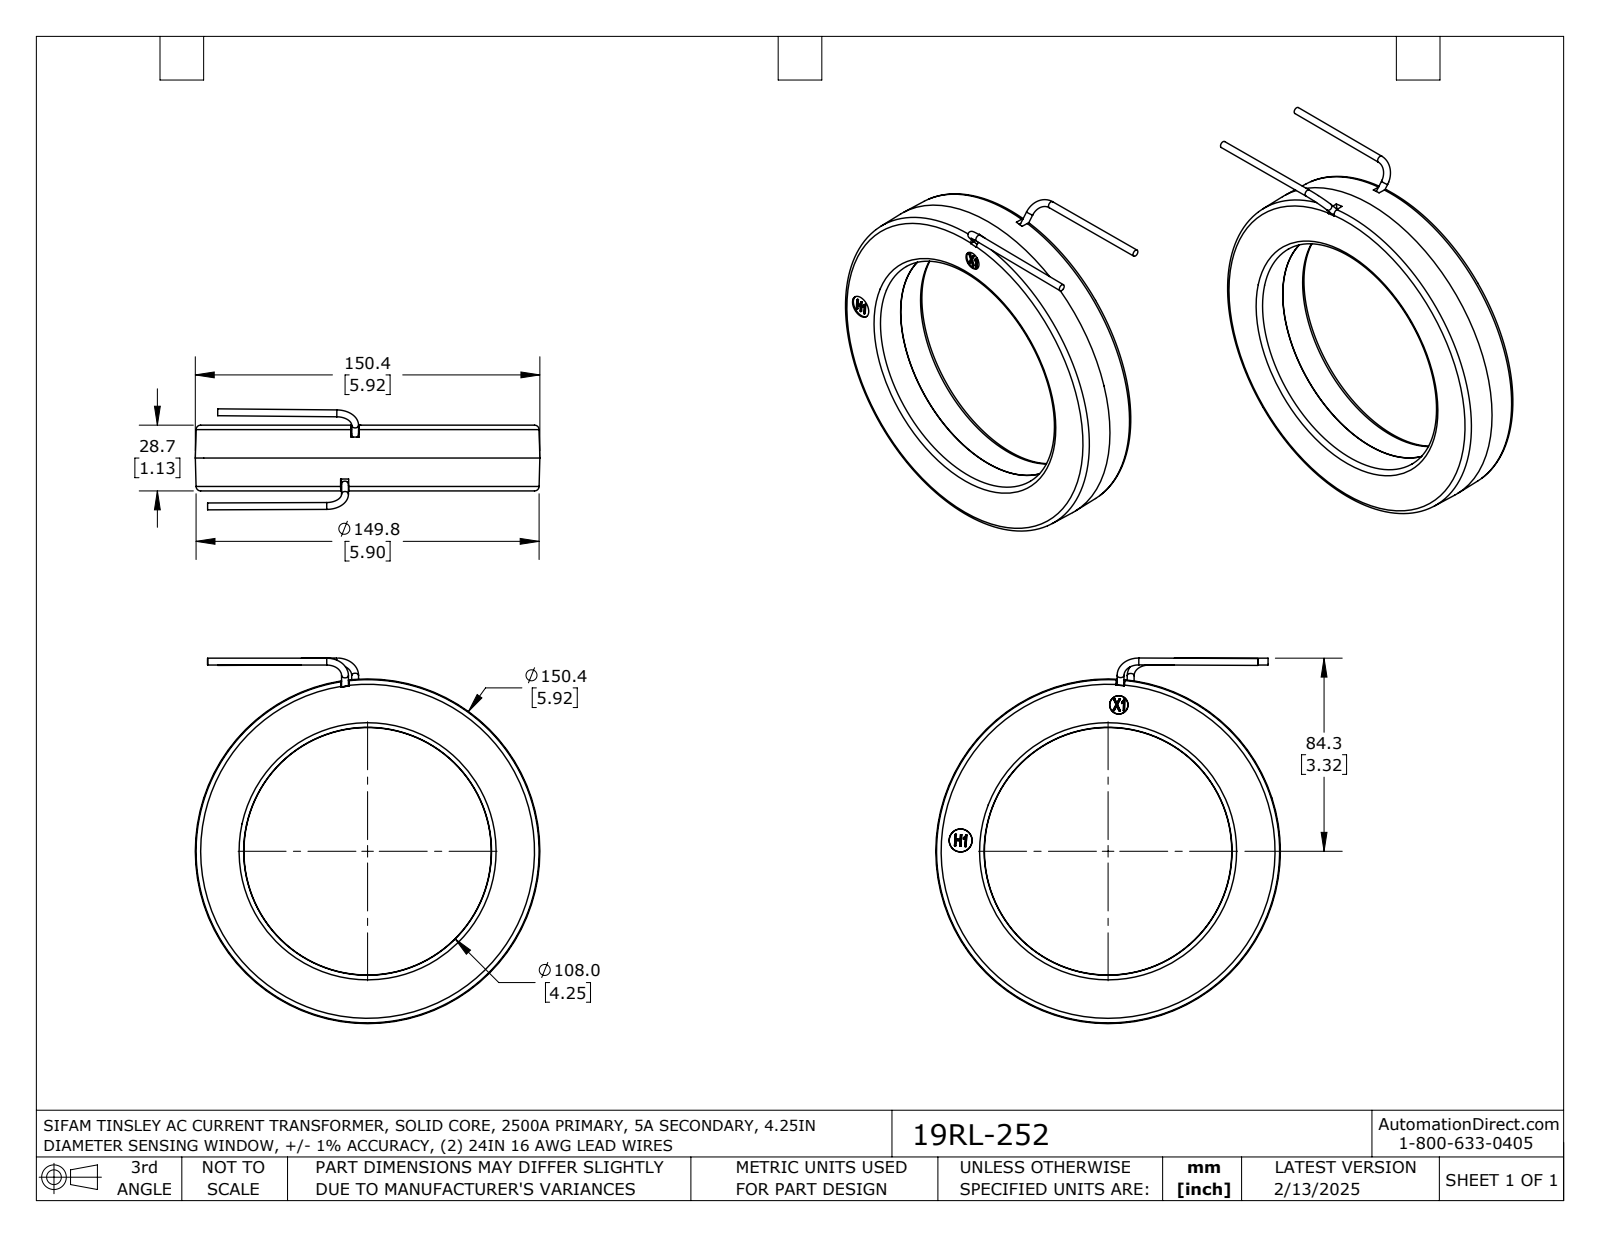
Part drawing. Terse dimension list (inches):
name: 19RL-252
written by: SolidWorks 2021 (AUTOMOTIVE_DESIGN)
unit: in
bodies: 1 solid, 104 faces (52 planar, 8 cylindrical, 44 other)
size: 6.282 × 5.922 × 1.734
volume: 14.81 in³; area: 85.38 in²
bosses: 4× ⌀0.118
face distances: 0.563, 0.567, 1.13, 1.111, 0.548, 0.544, 0.019, 1.109, 0.546, 0.542
